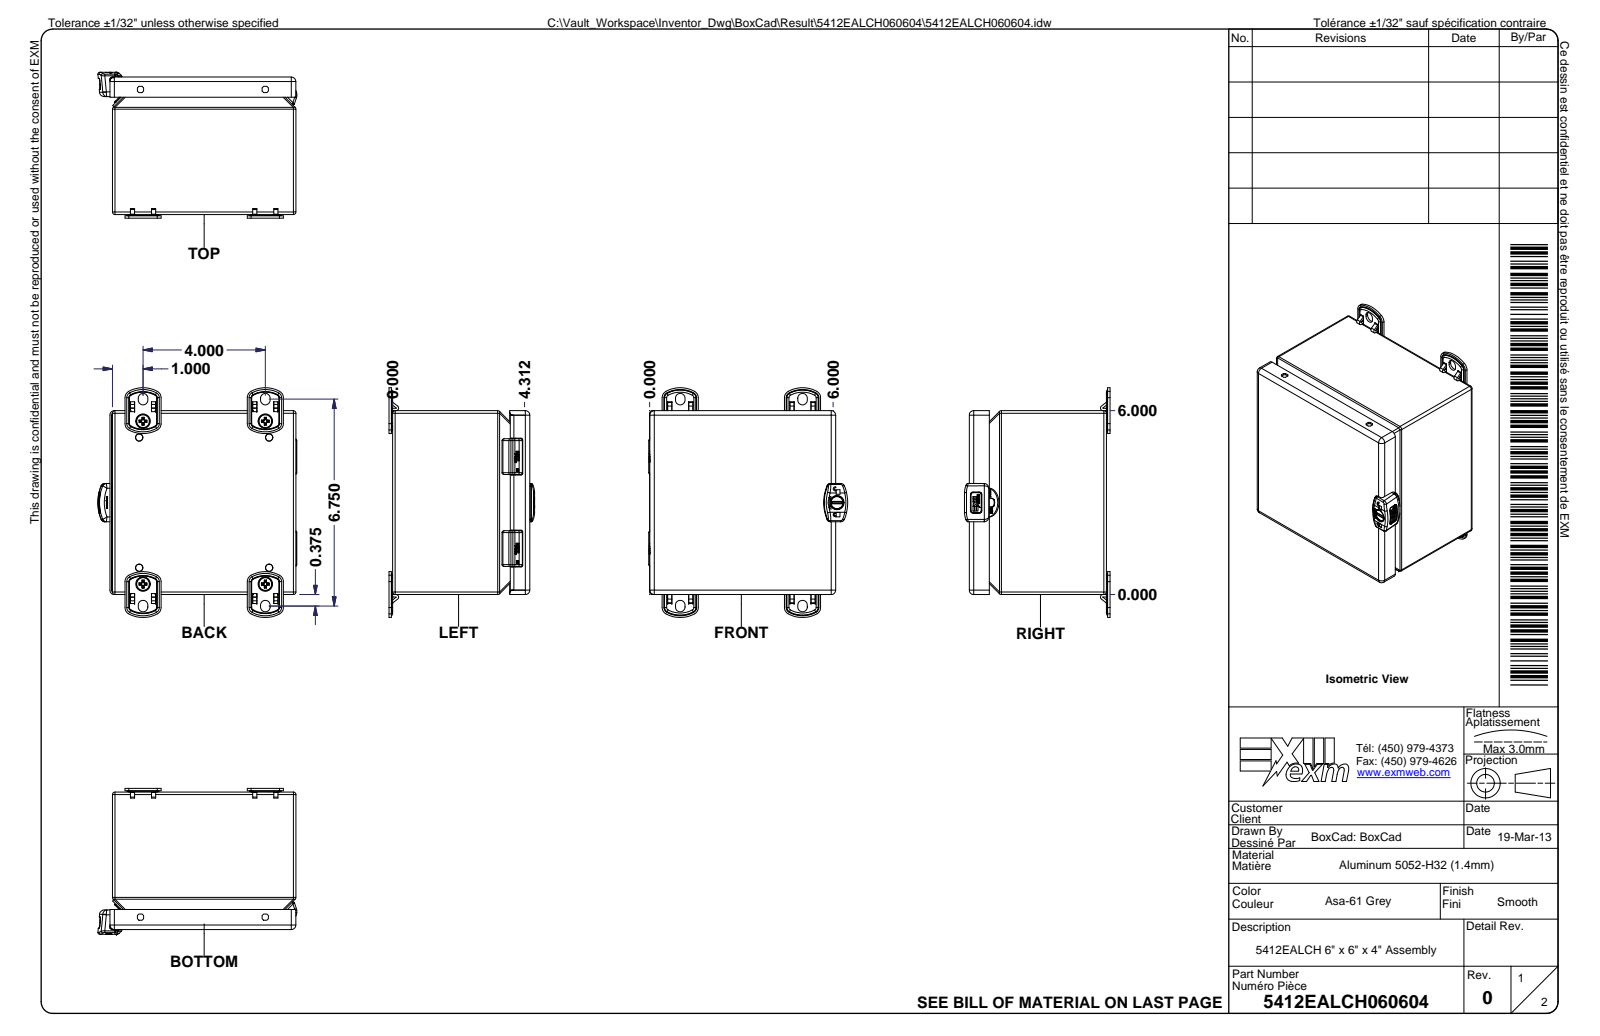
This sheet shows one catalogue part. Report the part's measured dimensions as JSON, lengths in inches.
{"part_name": "5412EALCH060604; 5412EALCH060604B; 5412EALCH060604B-P; RIVET_NUT_SS_M6_FH_CE (+8 more)", "step_written_by": "Autodesk Inventor 2024 (AUTOMOTIVE_DESIGN)", "units": "inches", "bodies": {"solids": 50, "faces": 6272, "planar": 2802, "cylindrical": 1470, "other": 2000}, "overall_size": [7.496, 6.441, 4.756], "volume_in3": 14.72, "surface_area_in2": 527.6, "round_holes": [[0.197, 4], [0.197, 4], [0.236, 4], [0.32, 4], [0.03, 2], [0.165, 2], [0.173, 2], [0.175, 2], [0.201, 2], [0.218, 2], [0.23, 2], [0.236, 2]], "round_bosses_or_shafts": [[0.232, 8], [0.5, 4], [0.236, 4], [0.197, 3], [0.394, 2], [0.3, 2], [0.193, 2], [0.035, 2]], "partial_cylinders_radius": [[0.02, 175], [0.008, 157], [0.01, 88], [0.039, 77], [0.004, 70], [0.059, 56], [0.031, 31], [0.012, 24]], "face_to_face_distances": [0.053, 5.947, 4.429, 6, 5.894, 4.376, 4.482, 0.236, 0.304, 0.289], "hole_center_spacings": [4.25, 4.25, 0.546, 4.159, 4.782, 3, 6.01, 6.314]}
